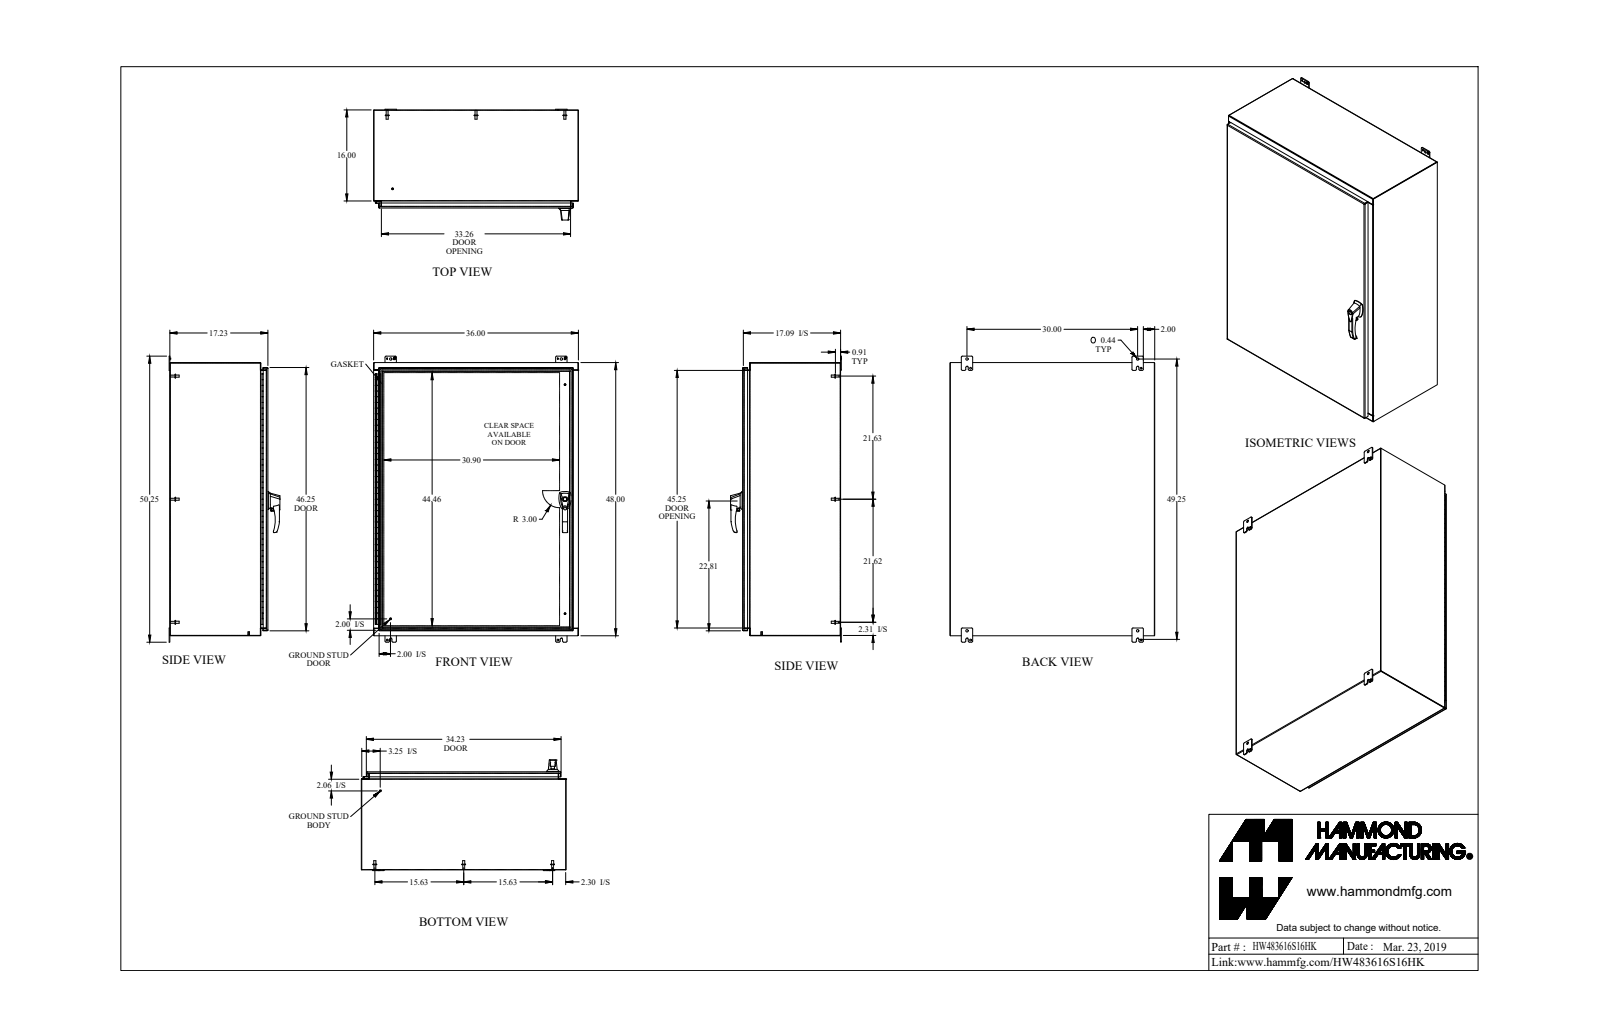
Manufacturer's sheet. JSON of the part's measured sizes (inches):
{"part_name": "HW483616S16HK", "step_written_by": "SolidWorks 2018 (AUTOMOTIVE_DESIGN)", "units": "inches", "bodies": {"solids": 47, "faces": 1584, "planar": 736, "cylindrical": 712, "other": 136}, "overall_size": [50.25, 36, 19.473], "volume_in3": 555.4, "surface_area_in2": 13913, "round_holes": [[0.176, 6], [0.313, 4], [0.25, 3], [0.265, 3], [0.413, 3], [0.196, 2], [0.256, 2], [0.394, 2], [0.437, 2], [0.11, 1], [0.233, 1], [0.33, 1]], "round_bosses_or_shafts": [[0.375, 13], [0.65, 8], [0.332, 8], [0.25, 7], [0.156, 6], [1, 3], [0.63, 2], [0.51, 2]], "partial_cylinders_radius": [[0.25, 27], [0.188, 20], [0.036, 14], [0.108, 14], [0.06, 12], [0.125, 9], [0.218, 8], [0.03, 6]], "face_to_face_distances": [0.072, 17.138, 17.066, 0.095, 17.233, 17.161, 35.928, 47.928, 35.856, 36], "hole_center_spacings": [20.118, 20.119, 40.237, 1.11, 1.111, 20.119, 20.887, 30]}
